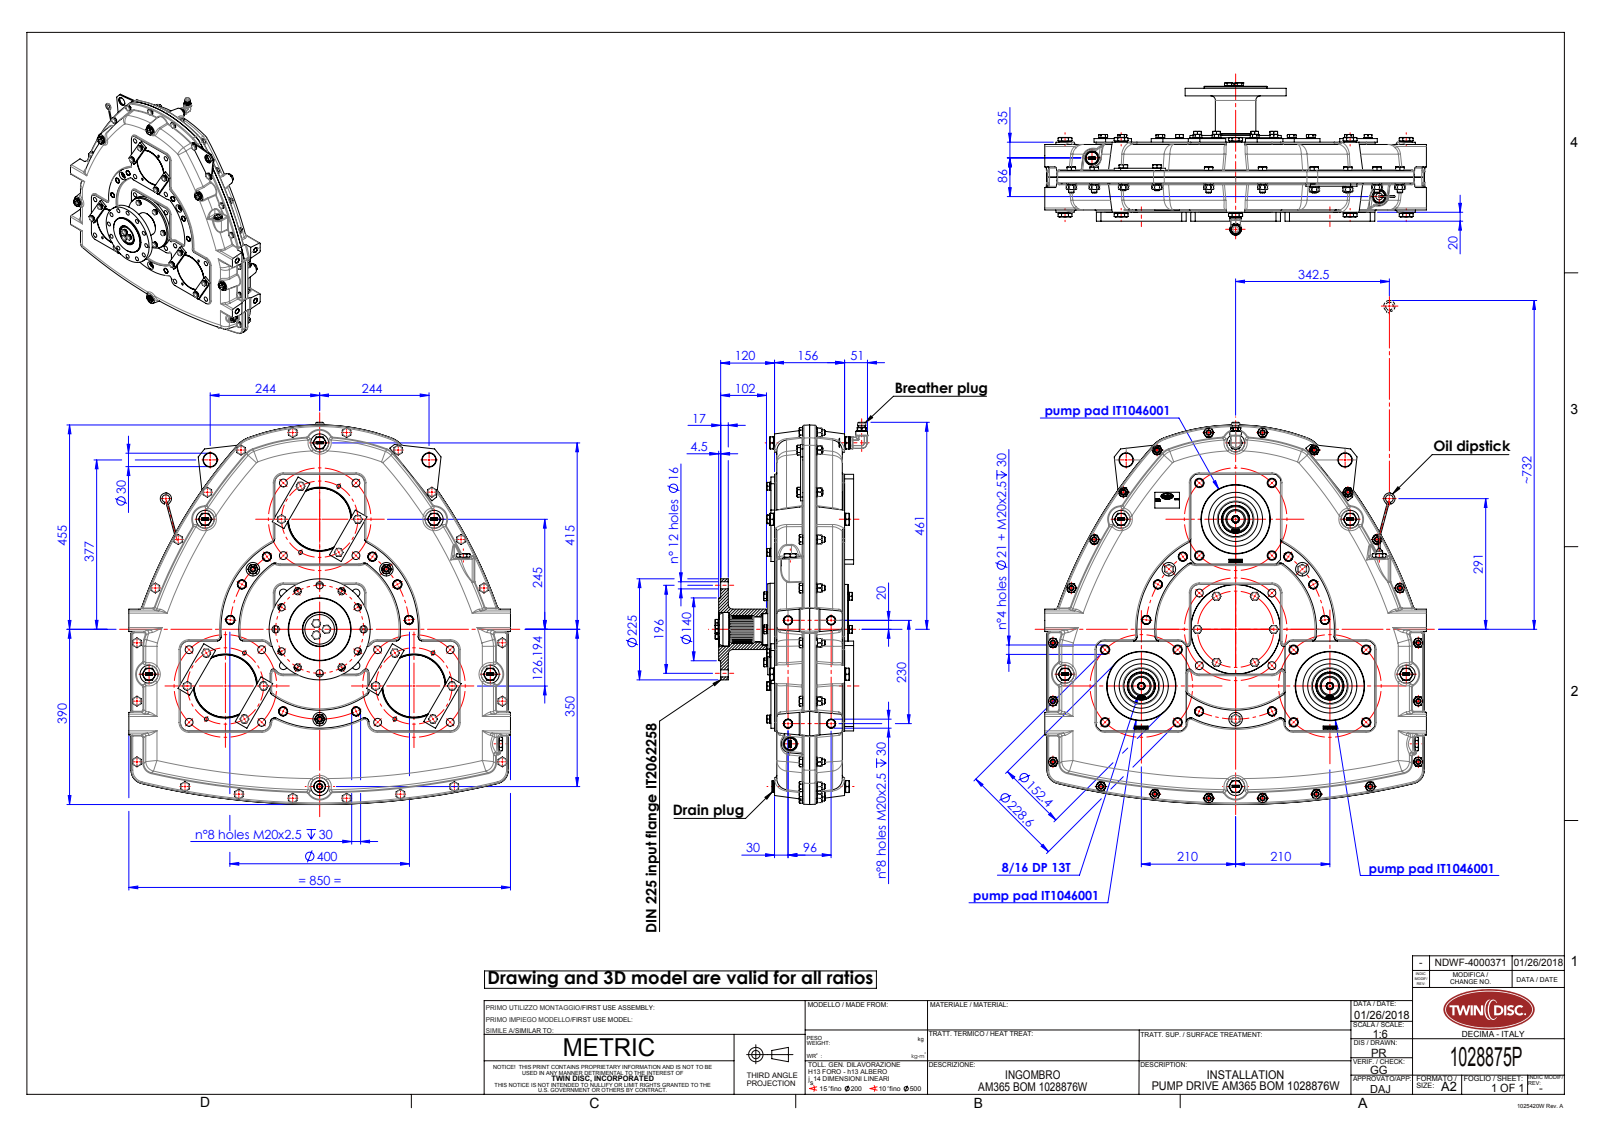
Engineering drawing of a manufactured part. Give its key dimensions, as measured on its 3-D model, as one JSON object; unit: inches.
{"part_name": "ITam365-002_rev00-installation; ITam365-001_rev01-installation; ITB01000000_rev01-installation; 1028875P (+8 more)", "step_written_by": "SolidWorks 2015 (AUTOMOTIVE_DESIGN)", "units": "inches", "bodies": {"solids": 150, "faces": 8932, "planar": 3777, "cylindrical": 2098, "other": 3057}, "overall_size": [33.496, 33.465, 13.354], "volume_in3": 4590, "surface_area_in2": 7925, "round_holes": [[0.512, 28], [0.689, 28], [0.335, 27], [0.48, 25], [0.827, 22], [0.402, 21], [0.406, 21], [0.433, 21], [0.63, 12], [0.787, 12], [0.733, 10], [0.472, 5]], "round_bosses_or_shafts": [[0.831, 25], [0.709, 25], [0.394, 22], [0.713, 21], [0.638, 21], [0.472, 21], [1.063, 10], [1.022, 9]], "partial_cylinders_radius": [[0.014, 58], [0.018, 58], [1.04, 58], [1.163, 58], [0.118, 36], [0.079, 30], [0.748, 28], [0.432, 25]], "face_to_face_distances": [2.874, 3.071, 0.197, 5.945, 5.748, 6.142, 0.787, 3.661, 2.283, 3.465], "hole_center_spacings": [13.638, 32.047, 3.274, 11.703, 9.257, 1.783, 2.591, 2.953]}
